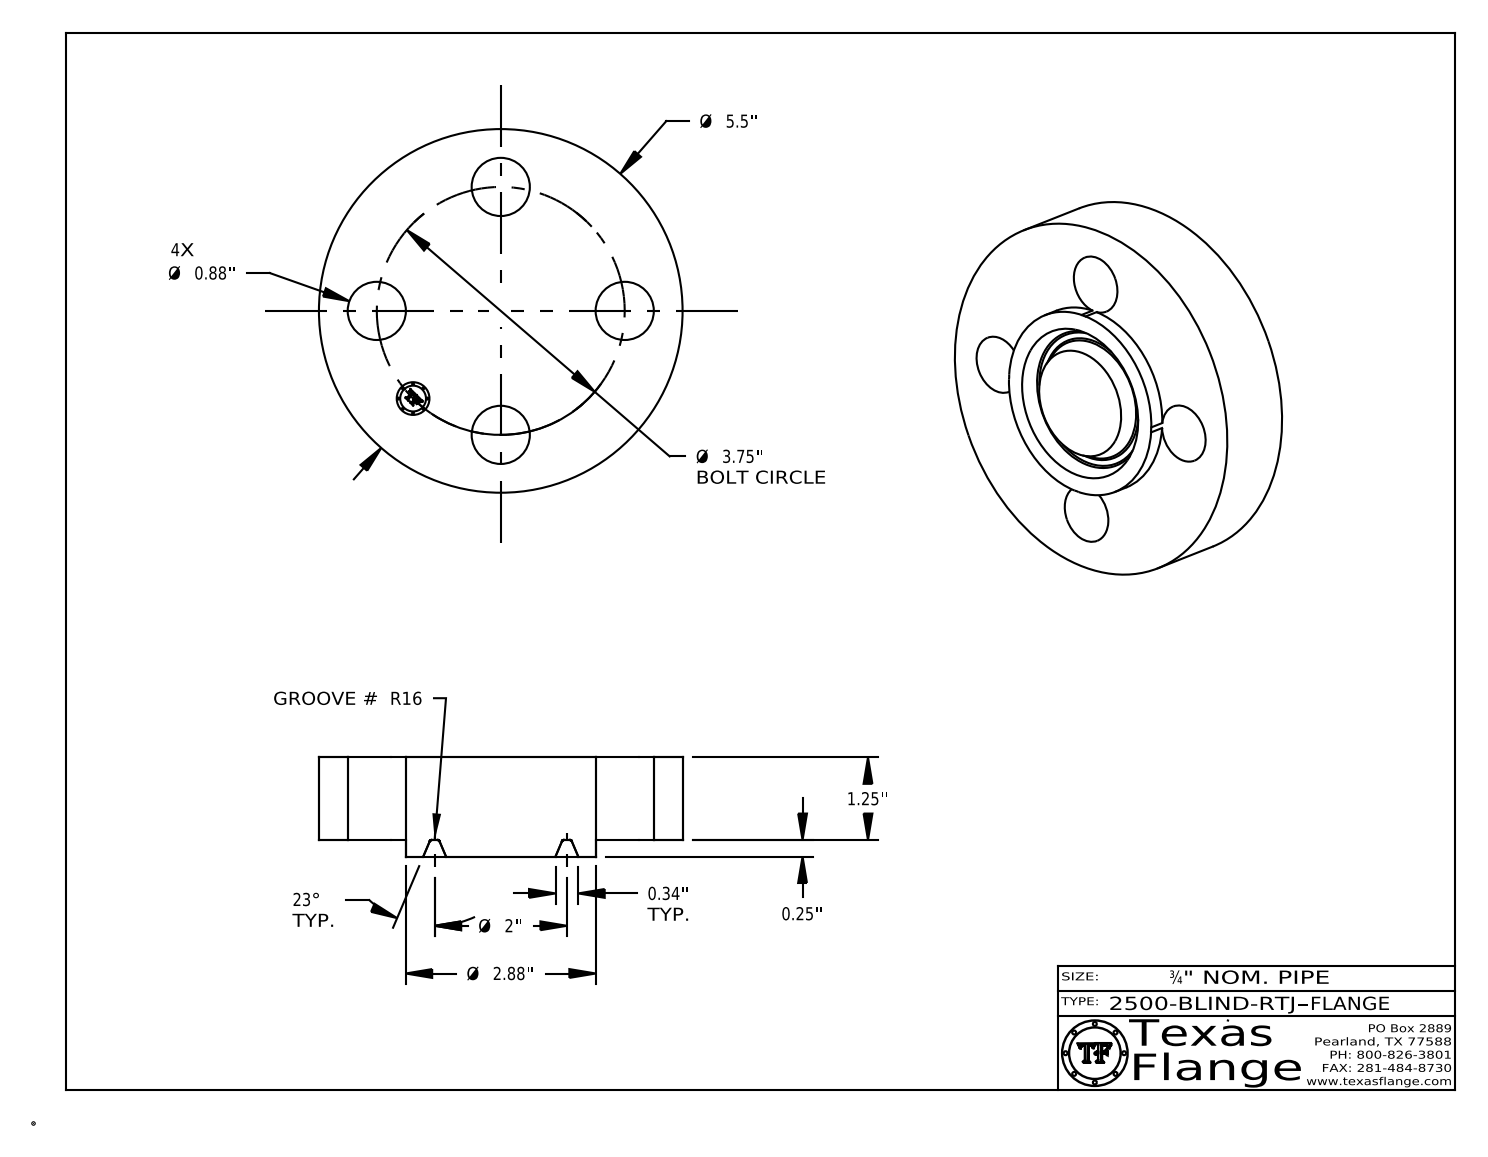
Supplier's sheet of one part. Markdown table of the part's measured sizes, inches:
| quantity | value |
| --- | --- |
| part name | 2500-BLIND-RTJ |
| STEP written by | CATIA V5 STEP AP214 (AUTOMOTIVE_DESIGN) |
| units | inches |
| bodies | 1 solid, 414 faces (370 planar, 36 cylindrical, 8 other) |
| overall size | 5.5 × 5.5 × 1.5 |
| volume | 27.91 in³ |
| surface area | 82.44 in² |
| round holes (diameter × count) | 0.88 × 4, 0.495 × 1 |
| round bosses / shafts (diameter × count) | 0.03 × 8, 5.5 × 1, 2.875 × 1, 0.39 × 1 |
| main face-to-face distances | 1.25, 0.25, 1.5, 1.485, 1.235, 0.015, 0.148, 0.144, 0.027, 0.096 |
| hole center spacings | 2.652, 1.435, 3.465, 3.75 |
